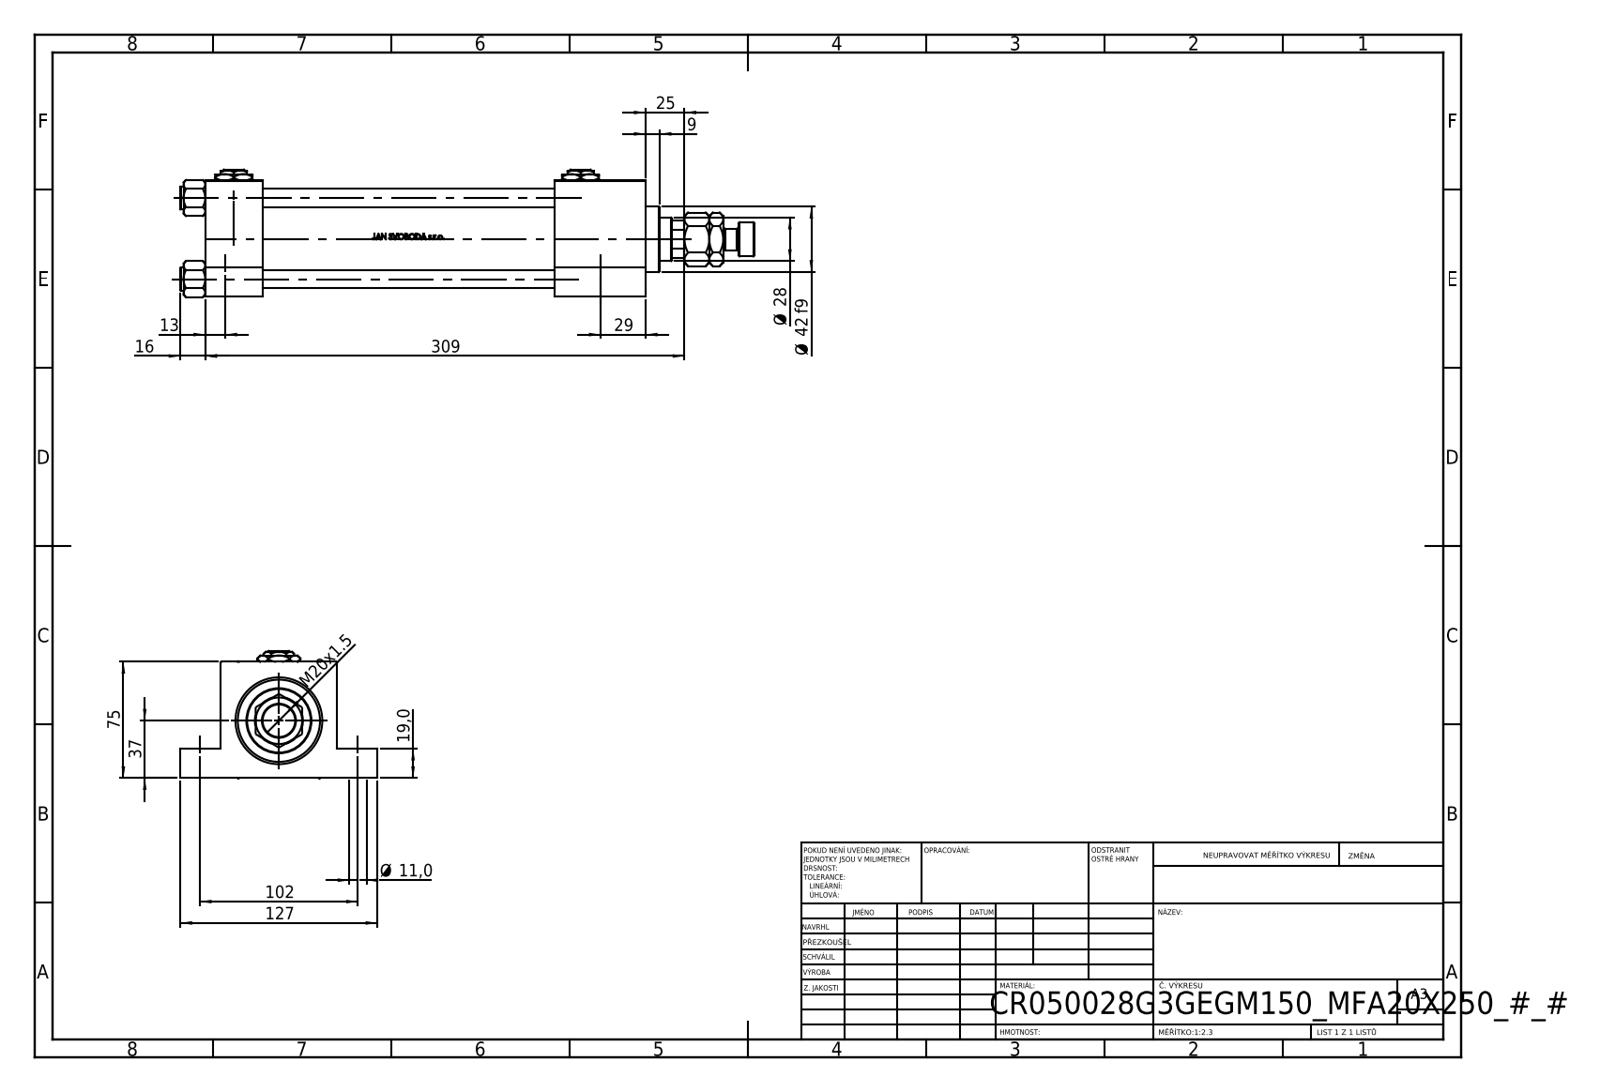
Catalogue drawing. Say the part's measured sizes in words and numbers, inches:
The part is named "V215CR_G_Body; MFA; V215CR_G_TYCINKA; V215CR_VCP_G (+3 more)". Its 3-D file was written by "SolidWorks 2019 (CONFIG_CONTROL_DESIGN)". It is 14 solids with 1224 faces: 492 planar, 128 cylindrical and 604 other. Overall it measures 14.567 by 5 by 3.239 inches. Its volume is 61.15 cubic inches and its surface area 381.1 square inches. Round holes: 4 of diameter 0.433, 4 of diameter 0.472, 2 of diameter 0.276, 2 of diameter 0.825, 2 of diameter 1.181, 1 of diameter 0.728, 1 of diameter 1.102, 1 of diameter 1.22, 1 of diameter 1.614, 1 of diameter 1.969, 1 of diameter 2.087. Round bosses or shafts: 4 of diameter 0.591, 1 of diameter 2.205, 1 of diameter 1.654, 1 of diameter 0.866, 1 of diameter 0.551. Partial cylindrical surfaces (rounded edges, fillets, slot ends): 1 of radius 0.531. The main face-to-face distances are 2.953, 1.457, 11.181, 9.724, 0.748, 2.205, 8.858, 7.402, 2.323, 1.024. The hole center spacings are 2.059, 1.442, 1.47, 2.02, 2.072, 2.912, 4.016, 9.237.
